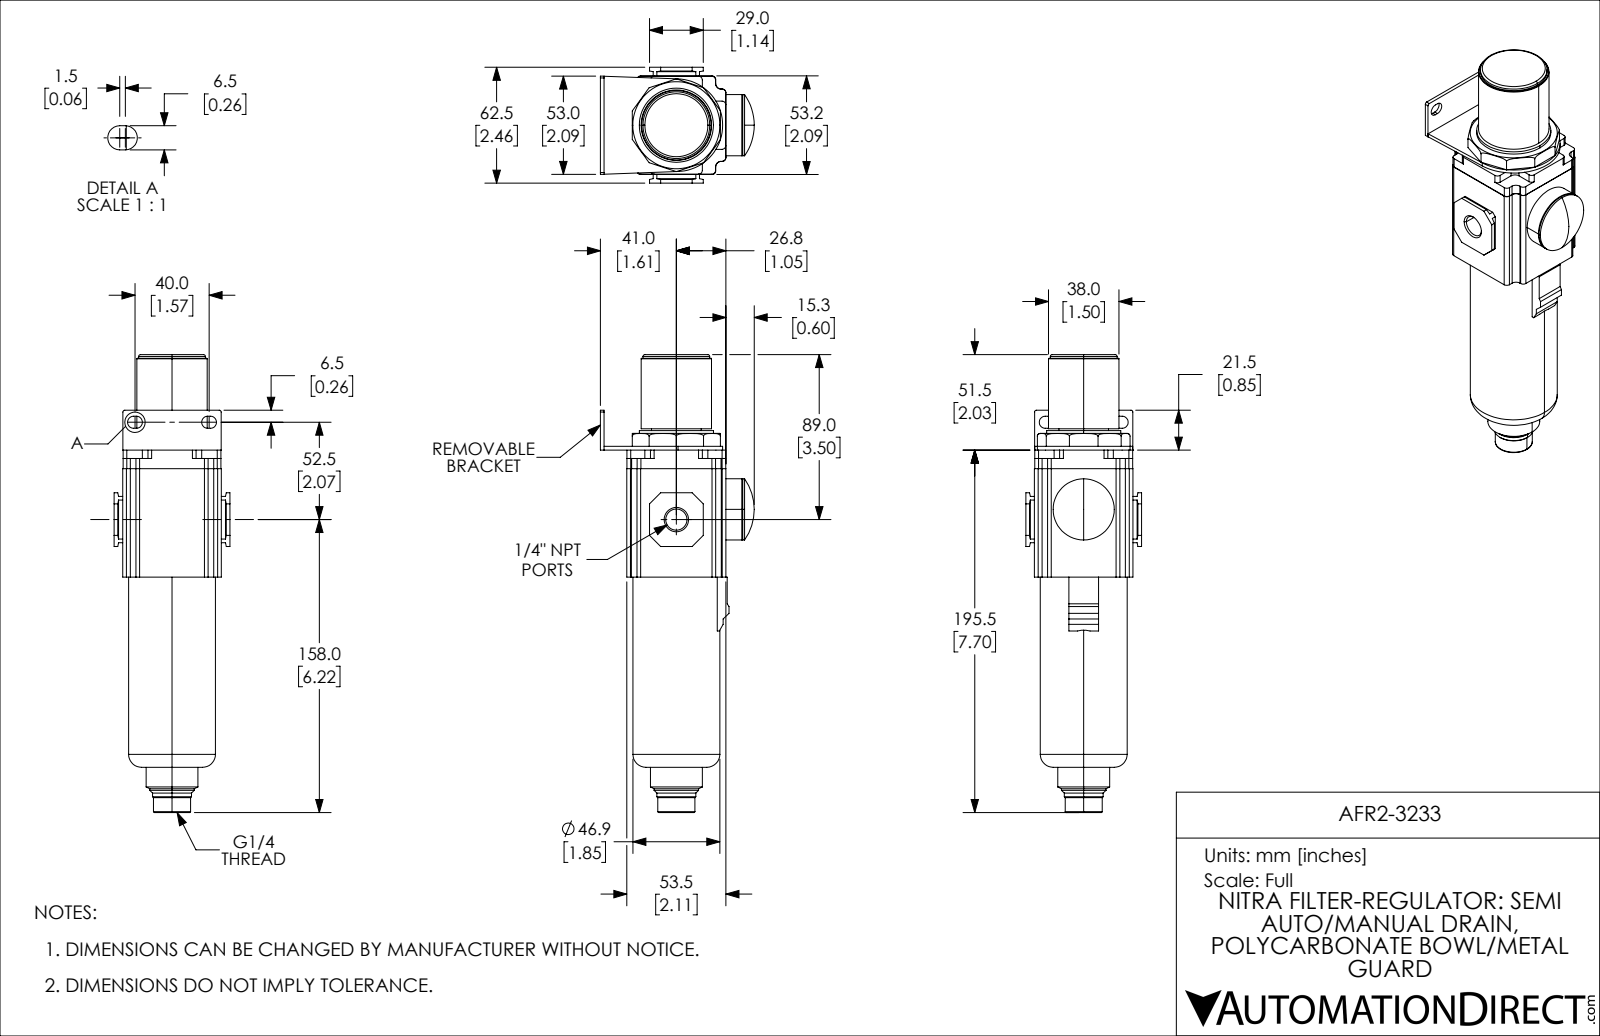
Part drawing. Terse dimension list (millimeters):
name: AFR2-3233
written by: SolidWorks 2019 (CONFIG_CONTROL_DESIGN)
unit: mm
bodies: 1 solid, 221 faces (124 planar, 71 cylindrical, 26 other)
size: 247 × 83.03 × 62.5
volume: 452 721 mm³; area: 51 631 mm²
holes: 2× ⌀11.45
bosses: 1× ⌀46.9, 1× ⌀40, 1× ⌀38, 1× ⌀36, 1× ⌀33, 1× ⌀28, 1× ⌀26.78, 1× ⌀24
rounds: 24× R2, 12× R3, 4× R3.25, 2× R1, 1× R25
face distances: 2, 53.2, 53.5, 4.65, 57.85, 14.25, 12.25, 67.75, 51.5, 49.5
